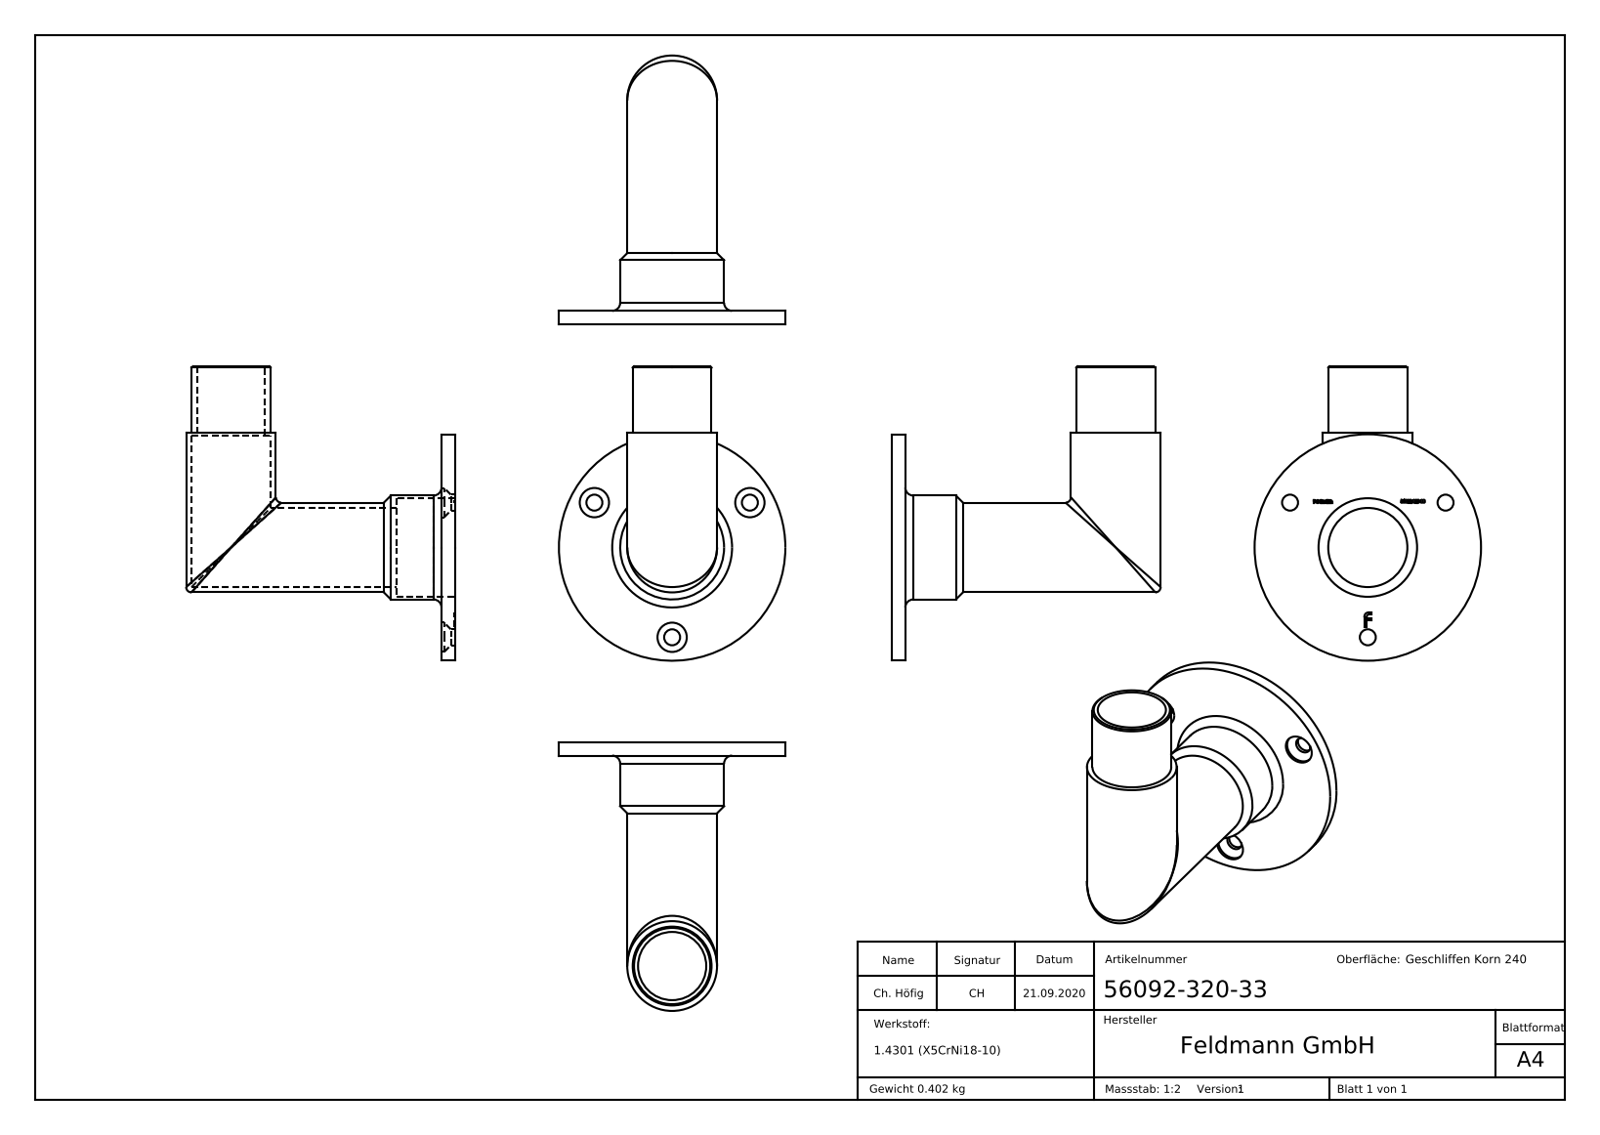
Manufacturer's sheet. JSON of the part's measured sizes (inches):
{"part_name": "56092-320-33", "step_written_by": "SolidWorks 2018 (CONFIG_CONTROL_DESIGN)", "units": "inches", "bodies": {"solids": 1, "faces": 310, "planar": 139, "cylindrical": 15, "other": 156}, "overall_size": [4.35, 3.97, 3.346], "volume_in3": 3.102, "surface_area_in2": 64.02, "round_holes": [[0.236, 3], [0.433, 3], [1.169, 2], [1.008, 1], [1.457, 1]], "round_bosses_or_shafts": [[1.327, 2], [3.346, 1], [1.535, 1], [1.165, 1]], "face_to_face_distances": [0.197, 0.866, 0.669, 0.039, 1.024, 0.984, 0.193, 0.862, 0.036, 0.99], "hole_center_spacings": [1.327, 2.298, 2.298]}
